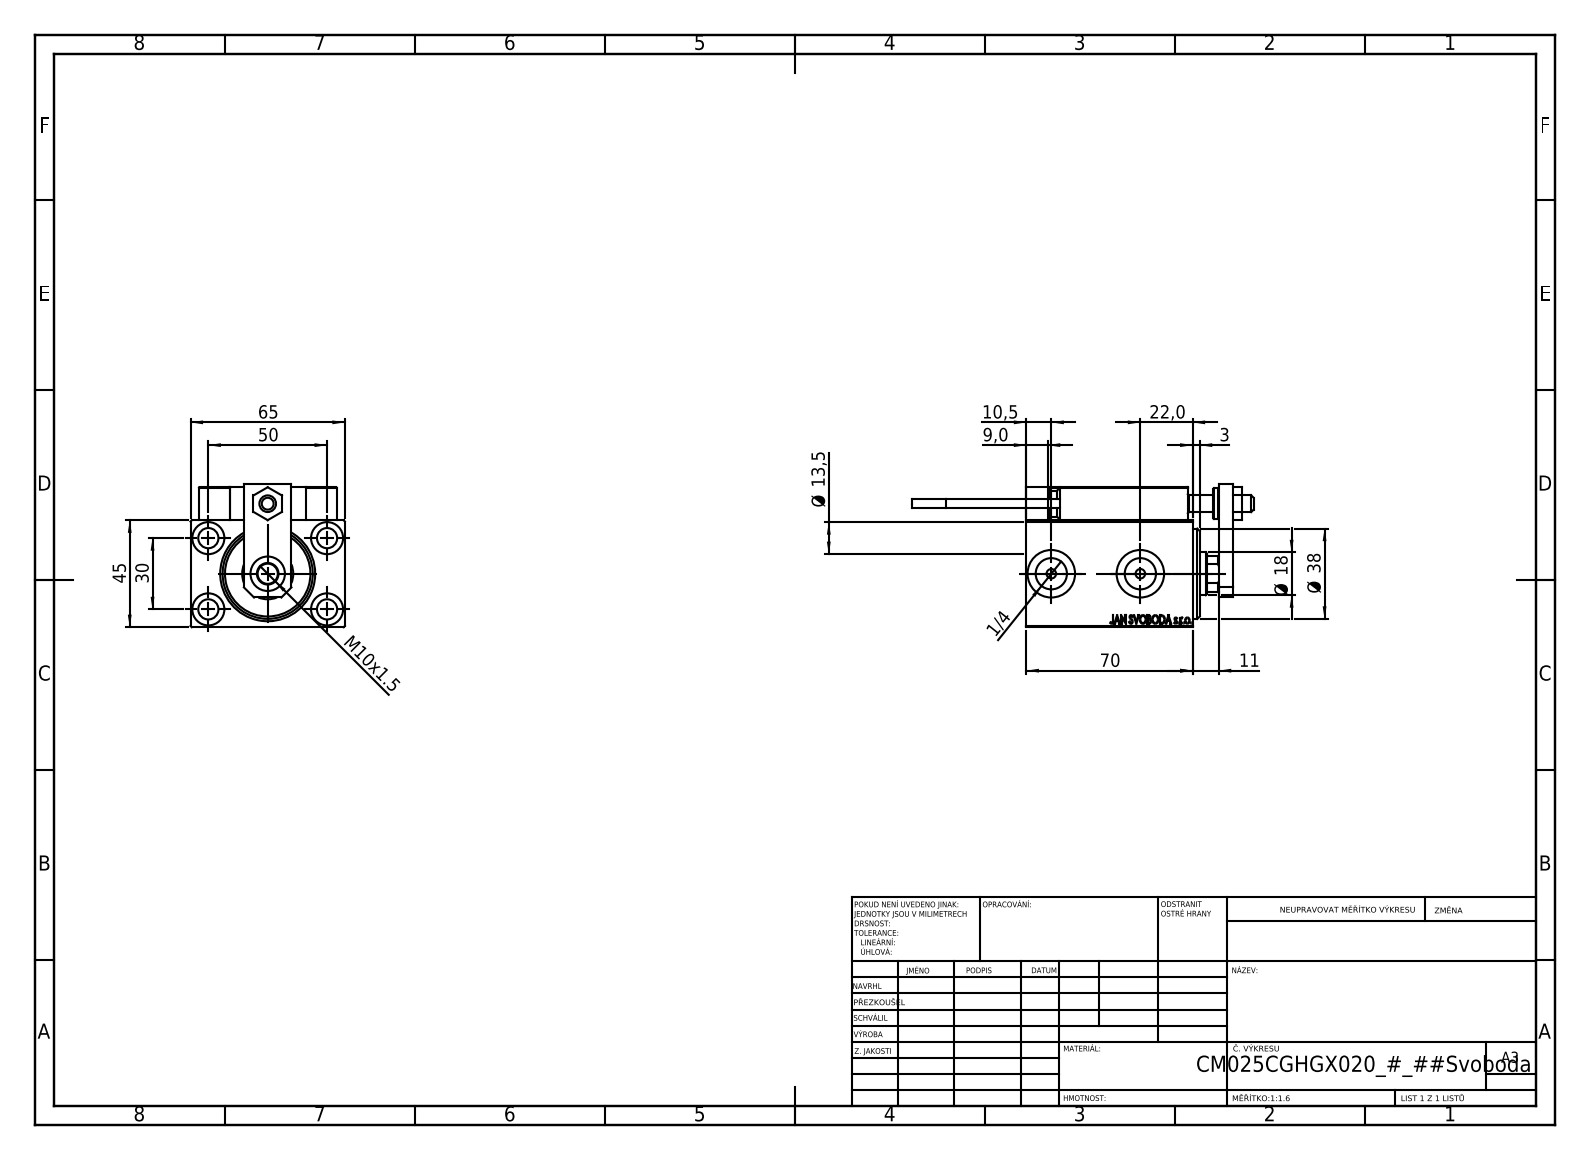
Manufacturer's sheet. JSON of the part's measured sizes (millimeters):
{"part_name": "SWITCH X; MAGNET; Block; ALLEN BOLT D5 (+7 more)", "step_written_by": "SolidWorks 2019 (CONFIG_CONTROL_DESIGN)", "units": "millimeters", "bodies": {"solids": 23, "faces": 1282, "planar": 560, "cylindrical": 188, "other": 534}, "overall_size": [143.7, 65, 60.5], "volume_mm3": 223110, "surface_area_mm2": 69190, "round_holes": [[4, 6], [8, 5], [8.5, 5], [3.2, 4], [13.5, 4], [5, 2], [13.16, 2], [20, 2], [7, 1], [14.5, 1], [18, 1], [21.5, 1]], "round_bosses_or_shafts": [[5, 2], [3.8, 2], [13, 1], [11, 1]], "partial_cylinders_radius": [[0.3, 30], [3, 2], [8.5, 1]], "face_to_face_distances": [45, 59, 14, 65, 6, 3, 19, 5, 13, 7], "hole_center_spacings": [29.15, 11.37, 20, 22.09, 28.9, 29.59, 29.69, 30]}
